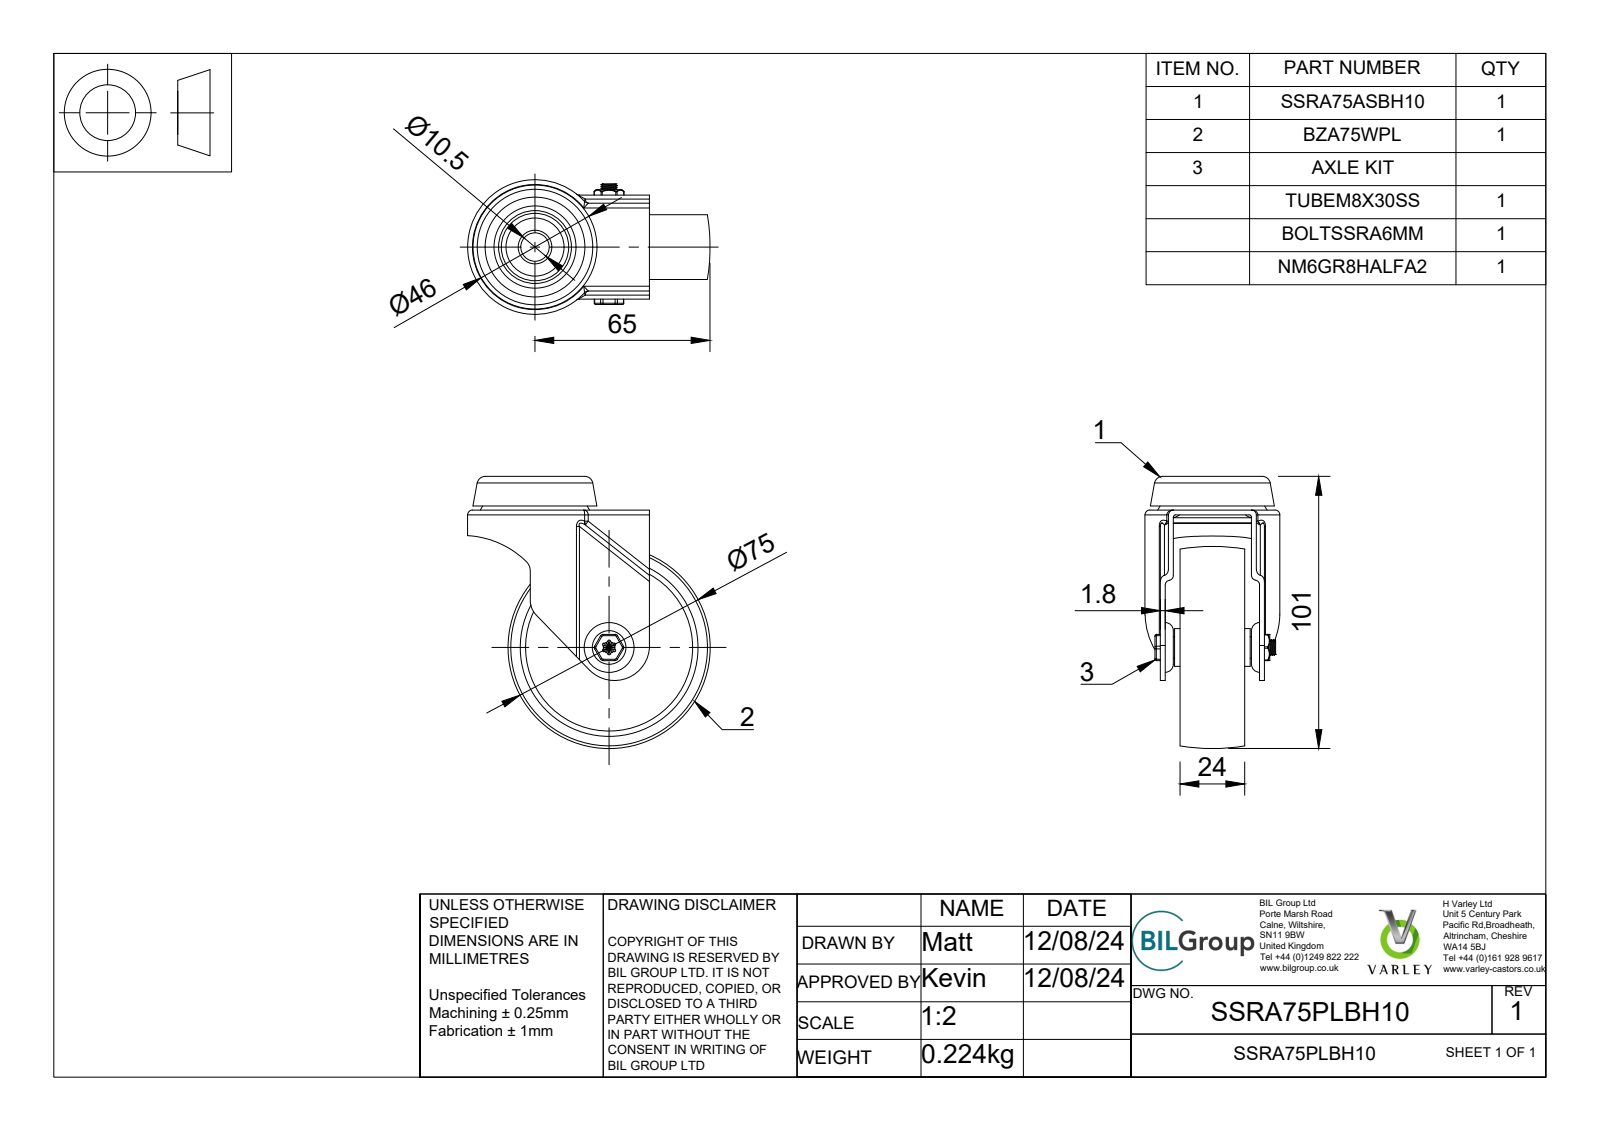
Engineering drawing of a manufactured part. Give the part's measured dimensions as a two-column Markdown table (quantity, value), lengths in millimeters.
| quantity | value |
| --- | --- |
| part name | SSRA75PLBH10 v3; SSRA75ASBH10 v1; ZINC PLATED PRESSED STEEL FORKS; ZINC PLATED PRESSED STEEL HEAD (+8 more) |
| STEP written by | Autodesk Translation Framework v13.14.0.145 (AUTOMOTIVE_DESIGN) |
| units | millimeters |
| bodies | 6 solids, 266 faces (54 planar, 98 cylindrical, 114 other) |
| overall size | 101 × 90 × 50 |
| volume | 65 160 mm³ |
| surface area | 48 484 mm² |
| round holes (diameter × count) | 6 × 1, 6.5 × 1, 8.2 × 1, 8.5 × 1, 10.5 × 1, 18 × 1, 19.5 × 1, 66 × 1 |
| round bosses / shafts (diameter × count) | 22 × 1, 14 × 1, 8 × 1, 7.9 × 1, 5 × 1 |
| partial cylindrical surfaces (radius × count) | 1 × 18, 1.8 × 14, 0.5 × 12, 0.4 × 6, 0.9 × 6, 2.12 × 1, 4.63 × 1, 8 × 1 |
| main face-to-face distances | 1.8, 4, 33.8, 3, 12.5, 17.3, 21.3, 10, 7.3, 31.3 |
